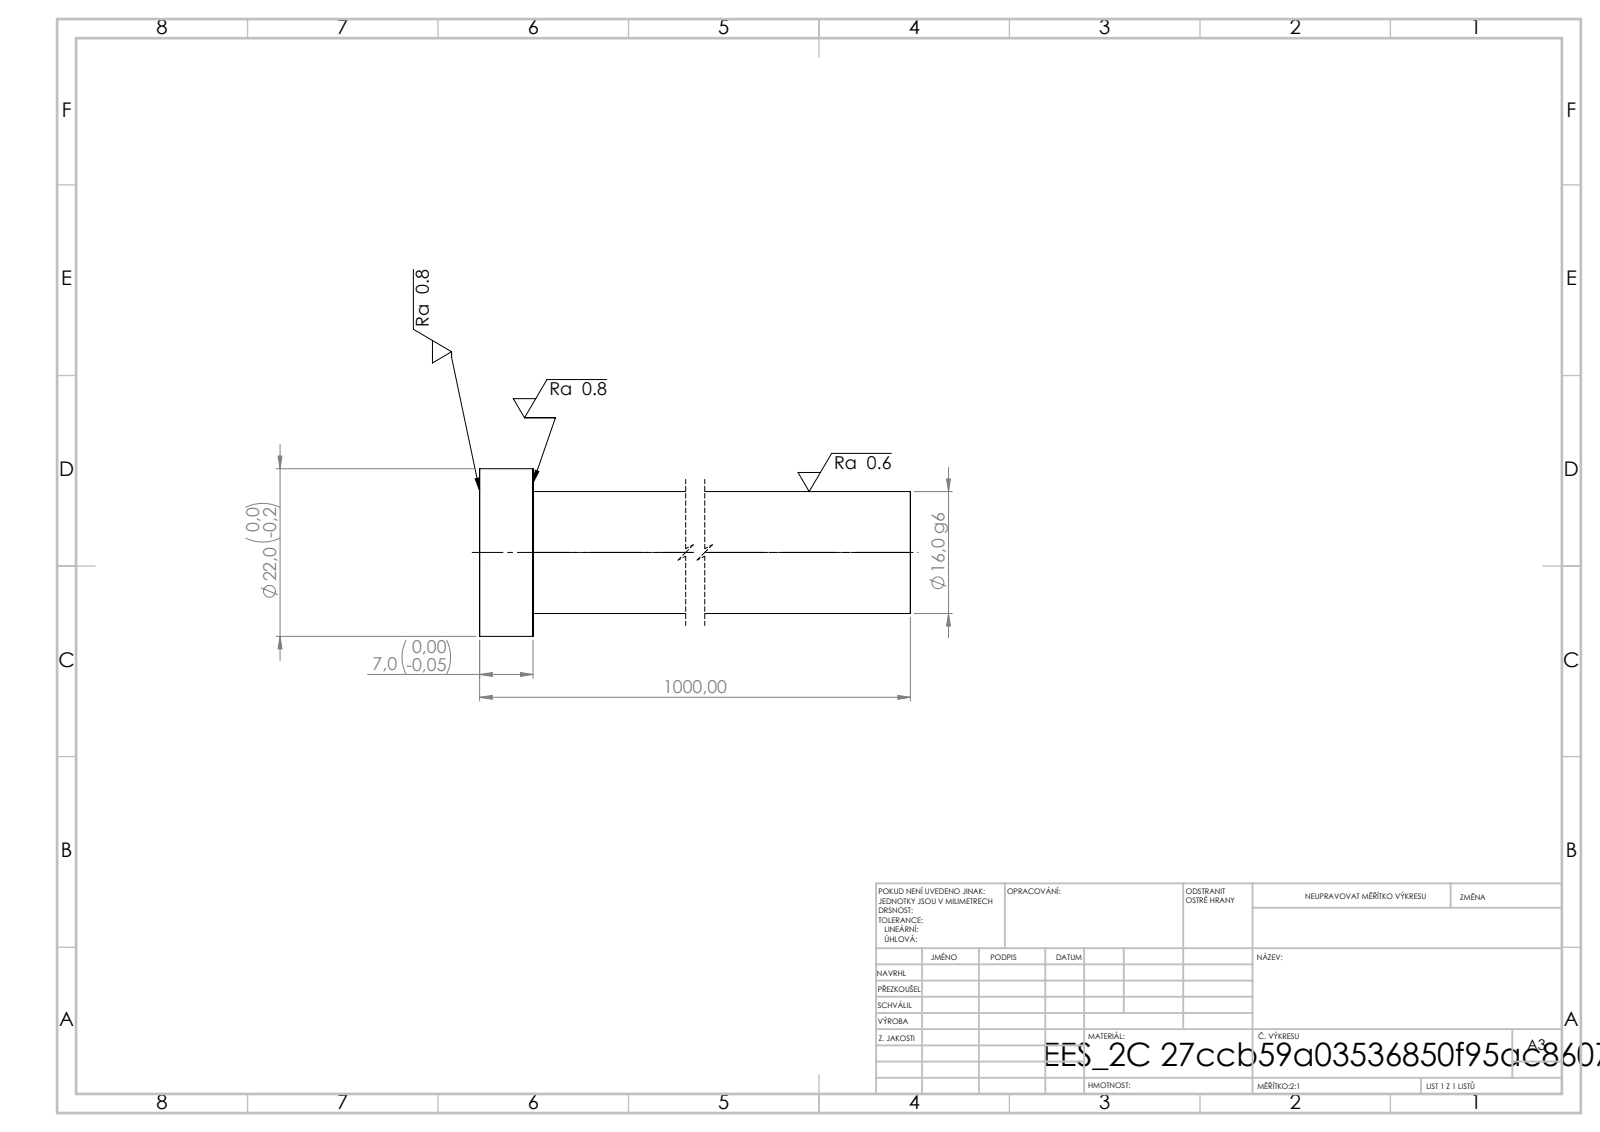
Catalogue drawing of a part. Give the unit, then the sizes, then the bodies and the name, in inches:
Units: inches
Overall size (bounding box): 39.37 × 0.866 × 0.866
Round bosses / shafts (diameter × count): ⌀0.866 ×1, ⌀0.63 ×1
Main face-to-face distances: 39.37, 0.276, 39.094
Volume: 12.35 in³ · Surface area: 79.3 in²
Bodies: 1 solid, 7 faces (3 planar, 4 cylindrical, 0 other)
STEP written by: SolidWorks 2019 (CONFIG_CONTROL_DESIGN)
